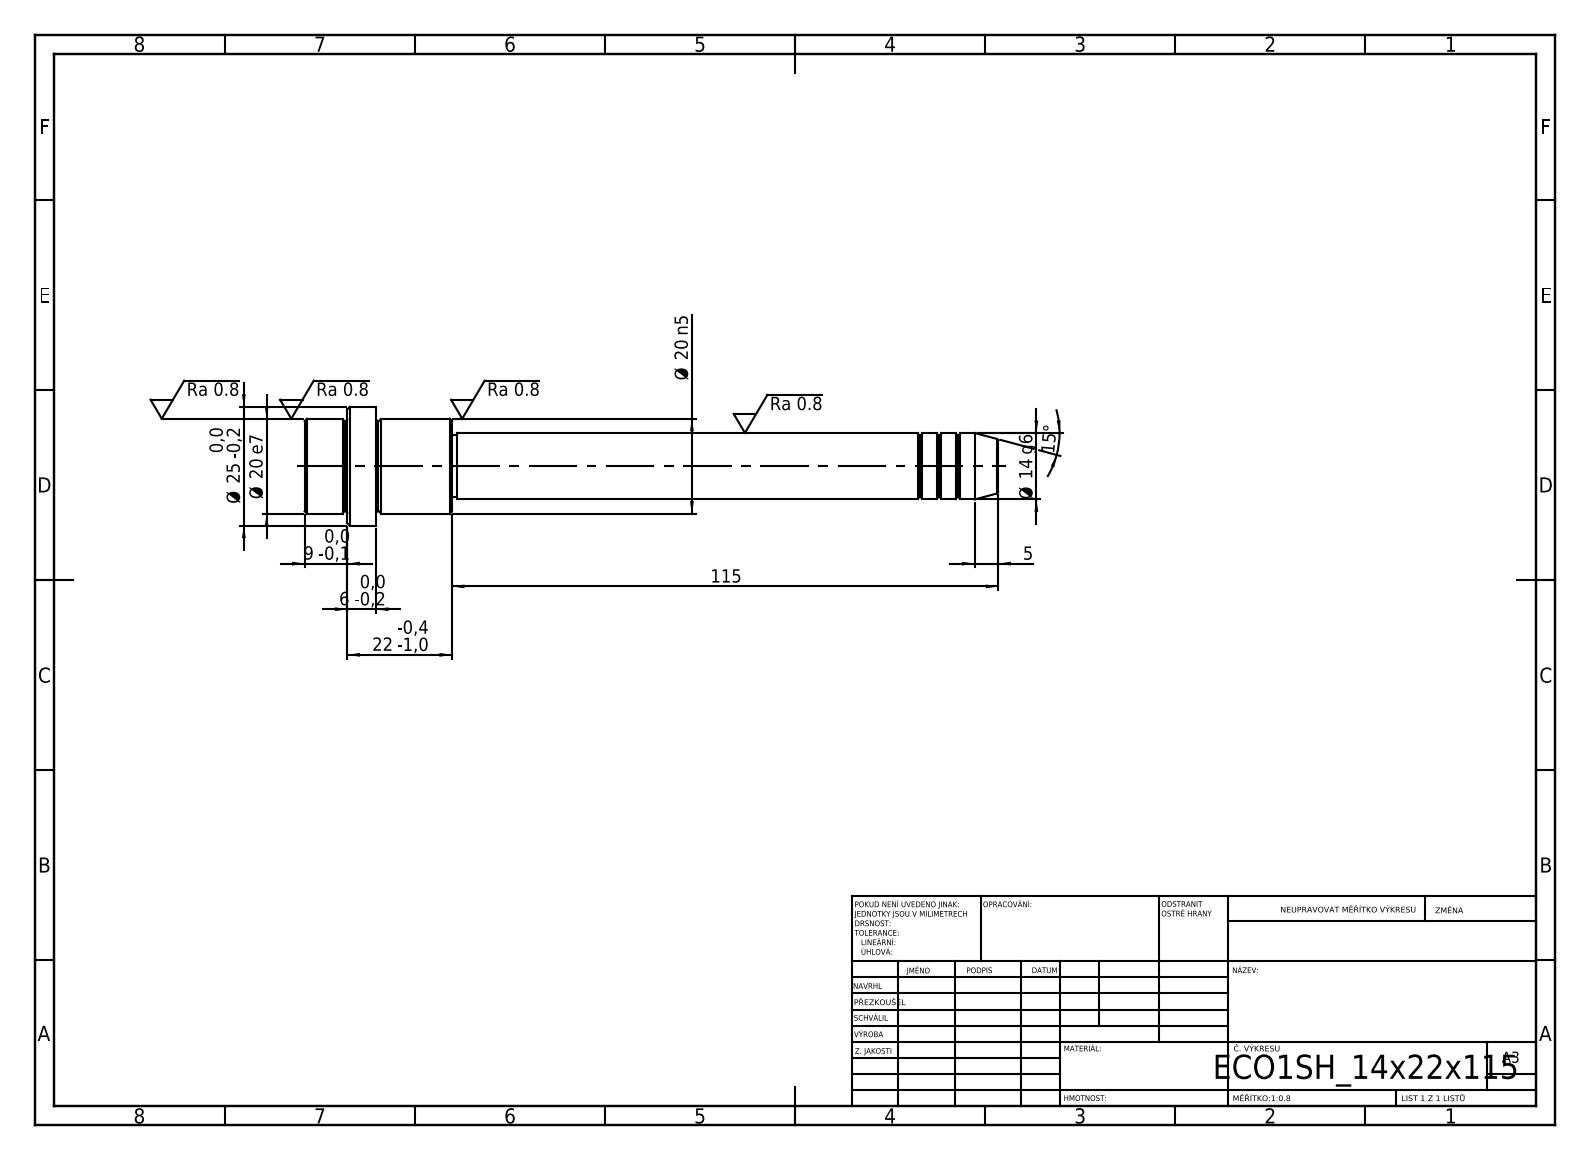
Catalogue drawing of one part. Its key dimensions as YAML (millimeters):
step_written_by: "SolidWorks 2019 (CONFIG_CONTROL_DESIGN)"
units: millimeters
bodies: {solids: 1, faces: 52, planar: 6, cylindrical: 16, other: 30}
overall_size: [146, 25, 25]
volume: 28218
surface_area: 8120
round_bosses_or_shafts:
  - {diameter: 25, count: 1}
  - {diameter: 20, count: 1}
  - {diameter: 14, count: 1}
  - {diameter: 13, count: 1}
face_to_face_distances: [15, 16, 31, 22, 6, 9, 115, 131, 137, 146]
